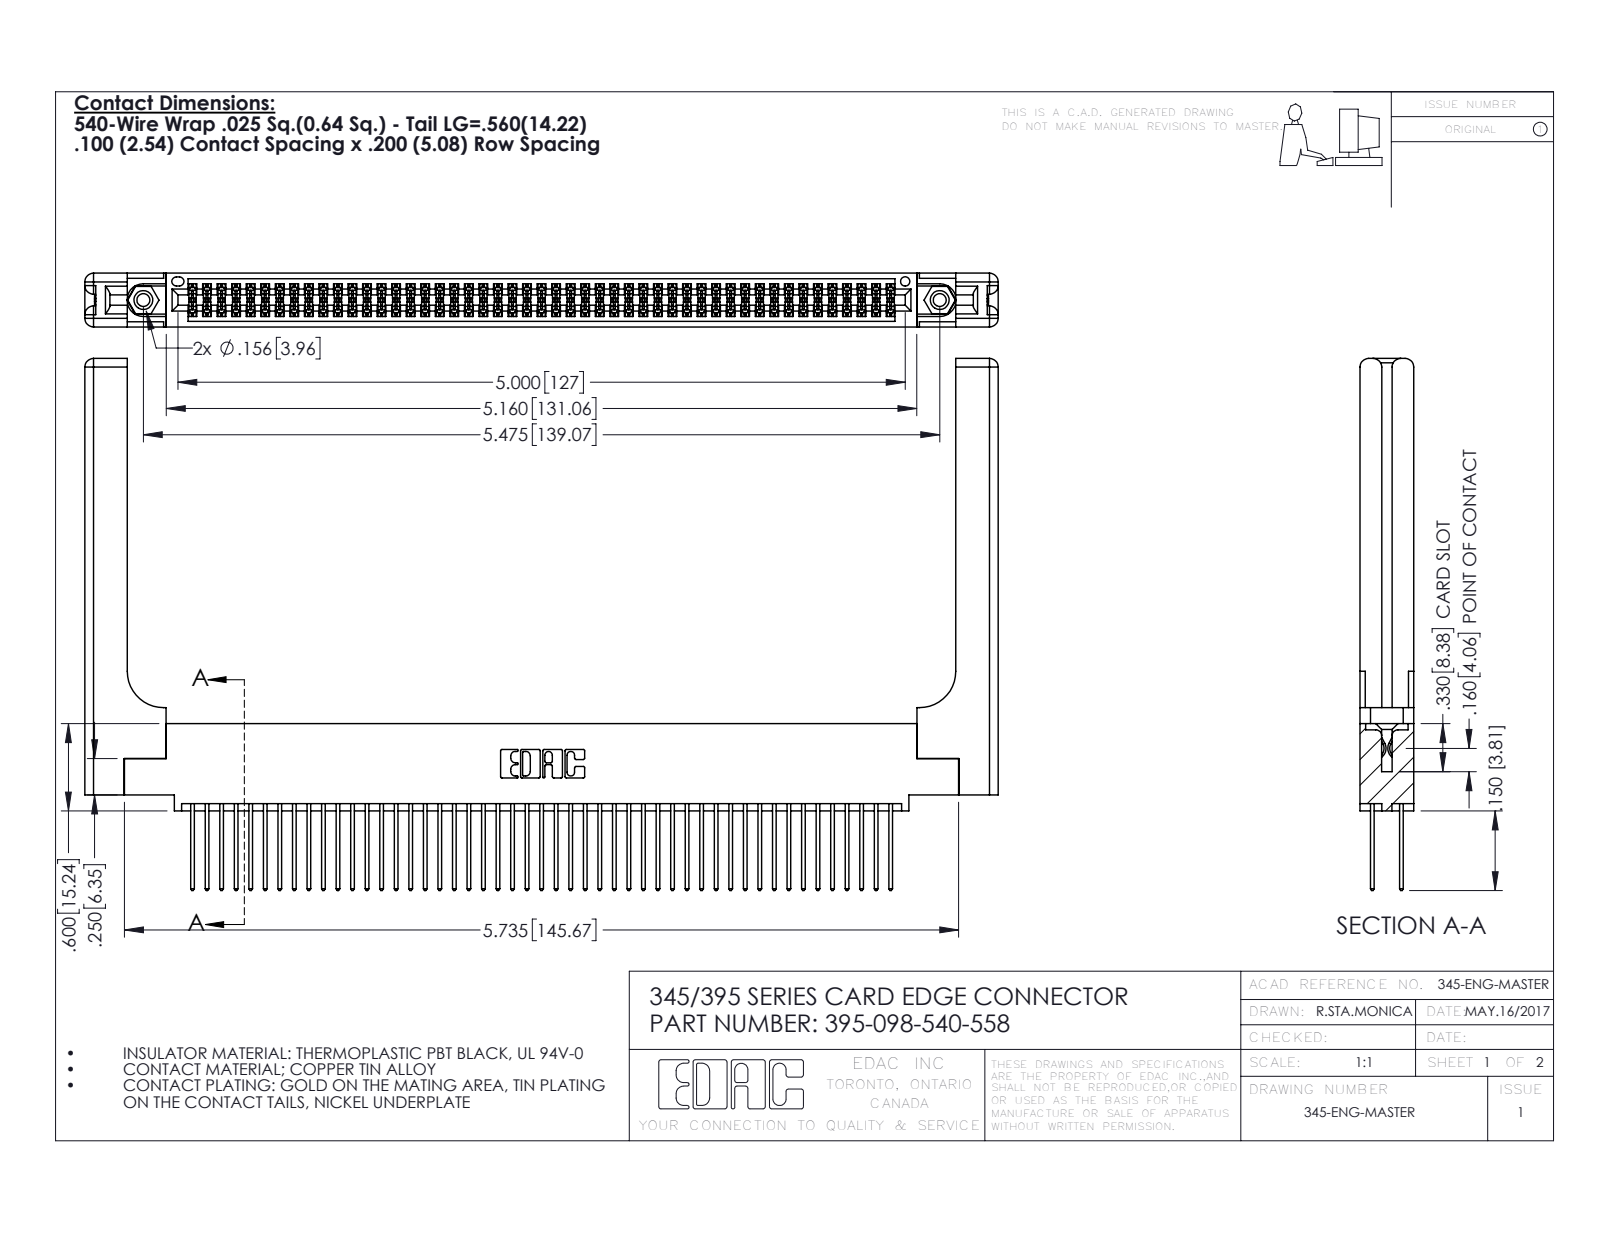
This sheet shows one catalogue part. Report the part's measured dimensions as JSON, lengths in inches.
{"part_name": "345 Part_0.110 Offset - 0.156 Dia-TH; 345-220-058_345-220-058; 345-250-001_345-250-001-102; 395-098-540-558 (+1 more)", "step_written_by": "SolidWorks 2016 (CONFIG_CONTROL_DESIGN)", "units": "inches", "bodies": {"solids": 103, "faces": 5286, "planar": 3466, "cylindrical": 1760, "other": 60}, "overall_size": [6.279, 3.657, 0.37], "volume_in3": 1.485, "surface_area_in2": 47.2, "round_holes": [[0.089, 2], [0.125, 2], [0.156, 2], [0.064, 1]], "round_bosses_or_shafts": [[0.155, 2]], "partial_cylinders_radius": [[0.006, 147], [0.01, 98], [0.01, 22], [0.06, 16], [0.007, 6], [0.031, 6], [0.026, 3], [0.014, 2]], "face_to_face_distances": [0.072, 0.298, 0.37, 0.098, 0.272, 0.025, 0.2, 0.225, 0.175, 0.148], "hole_center_spacings": [0.27, 5.239, 5.475]}
